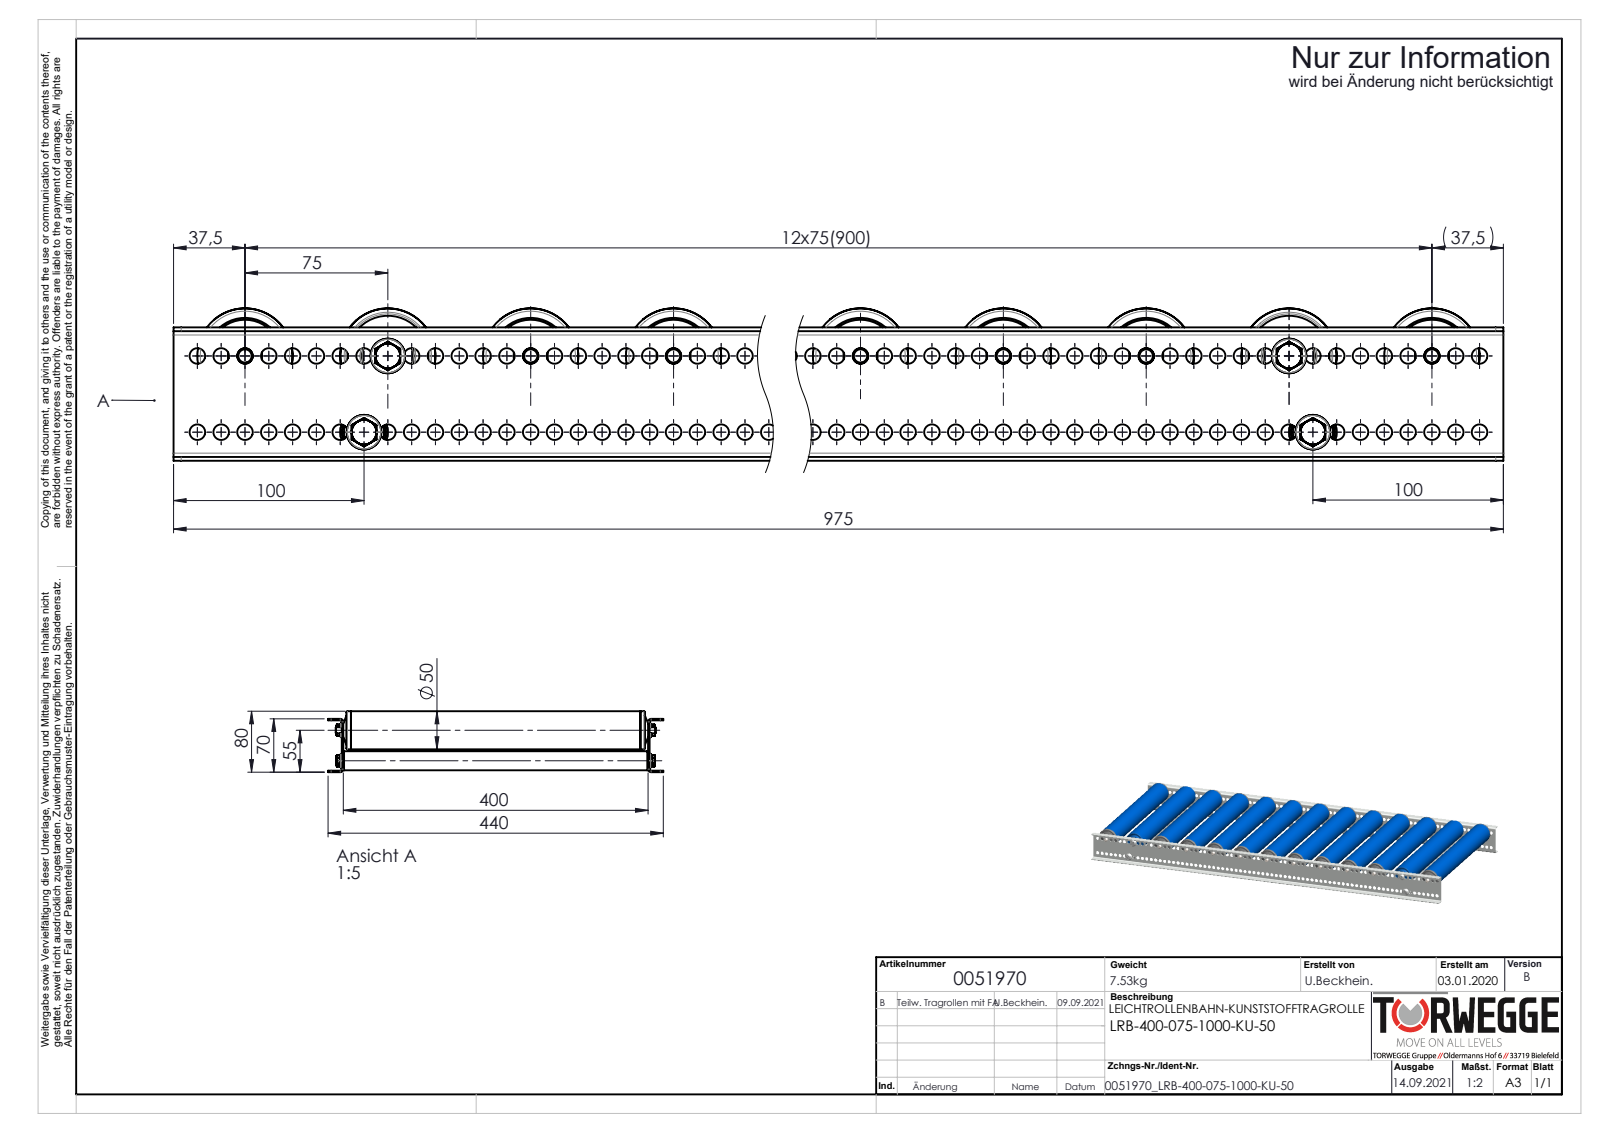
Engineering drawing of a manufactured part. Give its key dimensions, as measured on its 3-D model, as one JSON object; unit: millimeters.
{"part_name": "0026266_Typ-KUT100-50x2,8-12; 0017015_Tragrollenrohr-Ø50x2,8KU_KFG_0017015_L=380; 0017015_Tragrollenrohr-Ø50x2,8KU_KFG_0017015_L=385; 0024178_Passscheibe_DIN988_12x18x1 (+8 more)", "step_written_by": "SolidWorks 2020 (AUTOMOTIVE_DESIGN)", "units": "millimeters", "bodies": {"solids": 241, "faces": 4494, "planar": 1180, "cylindrical": 1912, "other": 1402}, "overall_size": [975, 440, 80], "volume_mm3": 3585000, "surface_area_mm2": 2687000, "round_holes": [[8.2, 154], [7.6, 11], [8, 11], [25, 11], [30, 11], [35, 11], [39.4, 11], [40, 11], [6.8, 4], [12, 2], [12.1, 2], [16, 2]], "round_bosses_or_shafts": [[50, 13], [44.4, 11], [38, 11], [36, 11], [33, 11], [22, 11], [21, 11], [25, 4]], "partial_cylinders_radius": [[0.6, 22], [0.75, 22], [2.45, 22], [4.87, 11], [7, 11], [4, 8], [2, 4], [2.5, 4]], "face_to_face_distances": [2, 402, 68, 400, 404, 66, 70, 392, 6, 12], "hole_center_spacings": [12.5, 25, 37.5, 50, 62.5, 75, 87.5, 100]}
